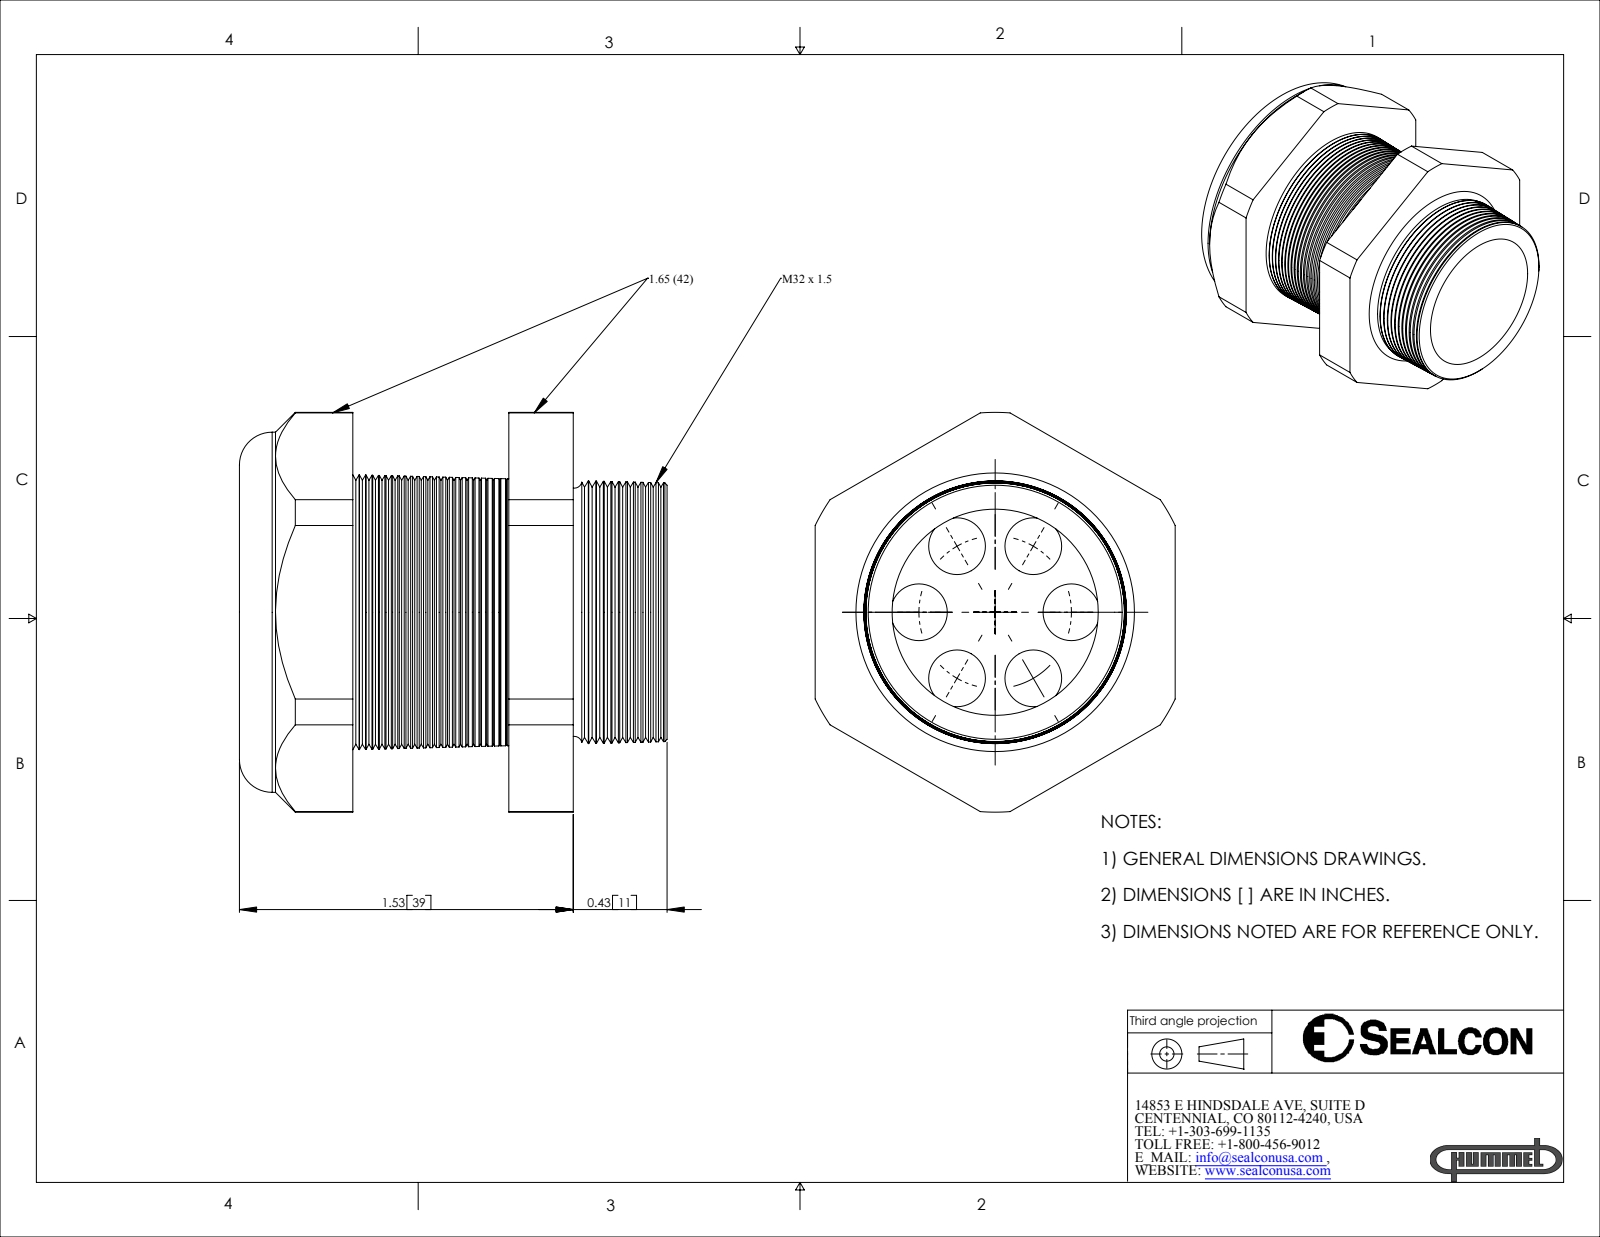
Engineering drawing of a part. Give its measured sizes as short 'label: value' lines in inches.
name: CD32M1-BK
written by: SolidWorks 2007 (CONFIG_CONTROL_DESIGN)
unit: in
bodies: 2 solids, 283 faces (21 planar, 32 cylindrical, 230 other)
size: 1.96 × 1.831 × 1.65
volume: 1.923 in³; area: 27.71 in²
holes: 6× ⌀0.26, 1× ⌀0.96, 1× ⌀0.98
bosses: 1× ⌀1.65
rounds: 1× R0.916
face distances: 0.715, 1.011, 0.295, 1.65, 0.52, 1.235, 1.53, 1.65, 0.5, 0.02
hole spacings: 0.35, 0.606, 0.699
